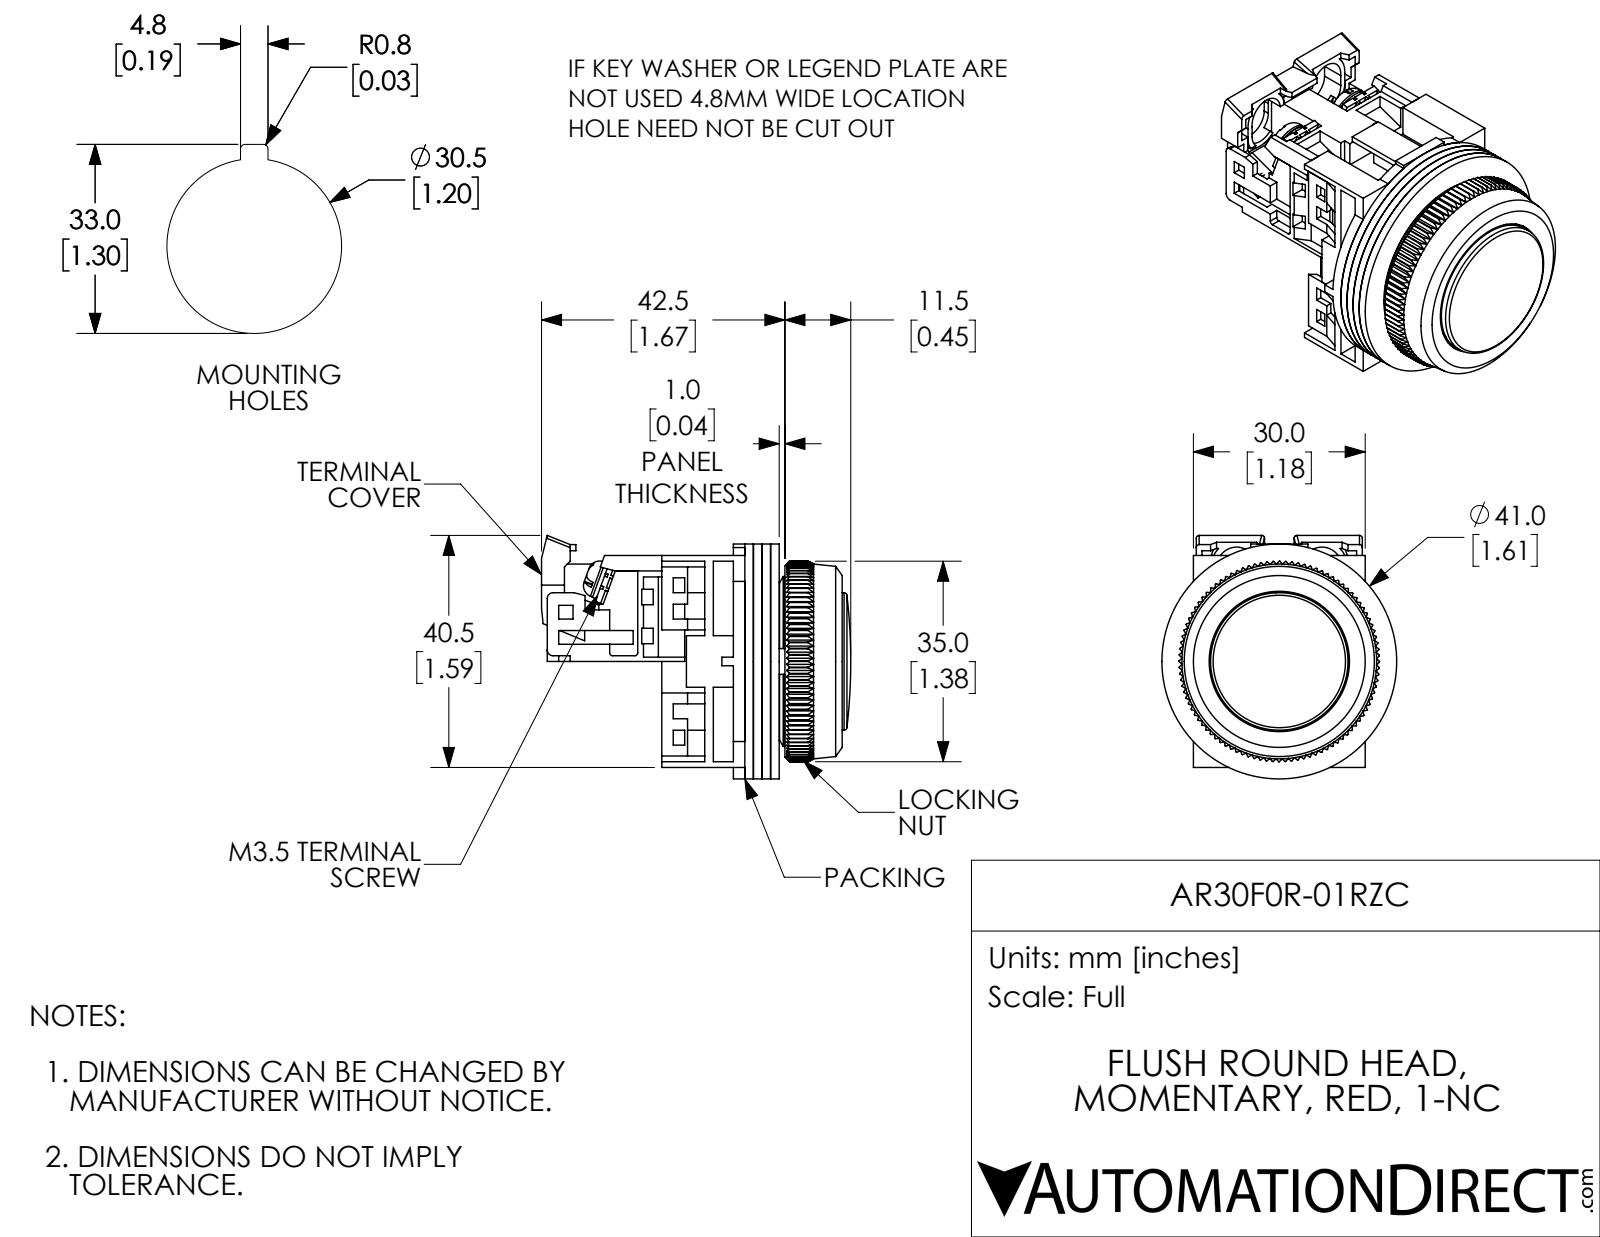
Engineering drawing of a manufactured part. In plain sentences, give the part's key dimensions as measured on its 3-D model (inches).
The part is named "AR30F0R-01RZC". Its 3-D file was written by "SolidWorks 2017 (AUTOMOTIVE_DESIGN)". It is 16 solids with 1258 faces: 798 planar, 249 cylindrical and 211 other. Overall it measures 2.125 by 1.673 by 1.614 inches. Its volume is 1.595 cubic inches and its surface area 47.89 square inches. Round holes: 4 of diameter 0.138, 2 of diameter 0.142, 1 of diameter 0.118, 1 of diameter 0.472, 1 of diameter 0.709, 1 of diameter 0.787, 1 of diameter 0.827, 1 of diameter 0.945, 1 of diameter 0.965, 1 of diameter 1.122, 1 of diameter 1.252. Round bosses or shafts: 2 of diameter 0.26, 2 of diameter 0.138, 1 of diameter 1.614, 1 of diameter 1.181, 1 of diameter 0.906, 1 of diameter 0.866, 1 of diameter 0.551. Partial cylindrical surfaces (rounded edges, fillets, slot ends): 8 of radius 0.059, 6 of radius 0.02, 2 of radius 0.039, 2 of radius 0.138, 2 of radius 0.177, 1 of radius 0.118, 1 of radius 0.398, 1 of radius 0.449. The main face-to-face distances are 0.059, 0.118, 0.177, 0.039, 0.197, 0.079, 0.689, 1.417, 0.256, 0.138. The hole center spacings are 0.579, 0.61.
